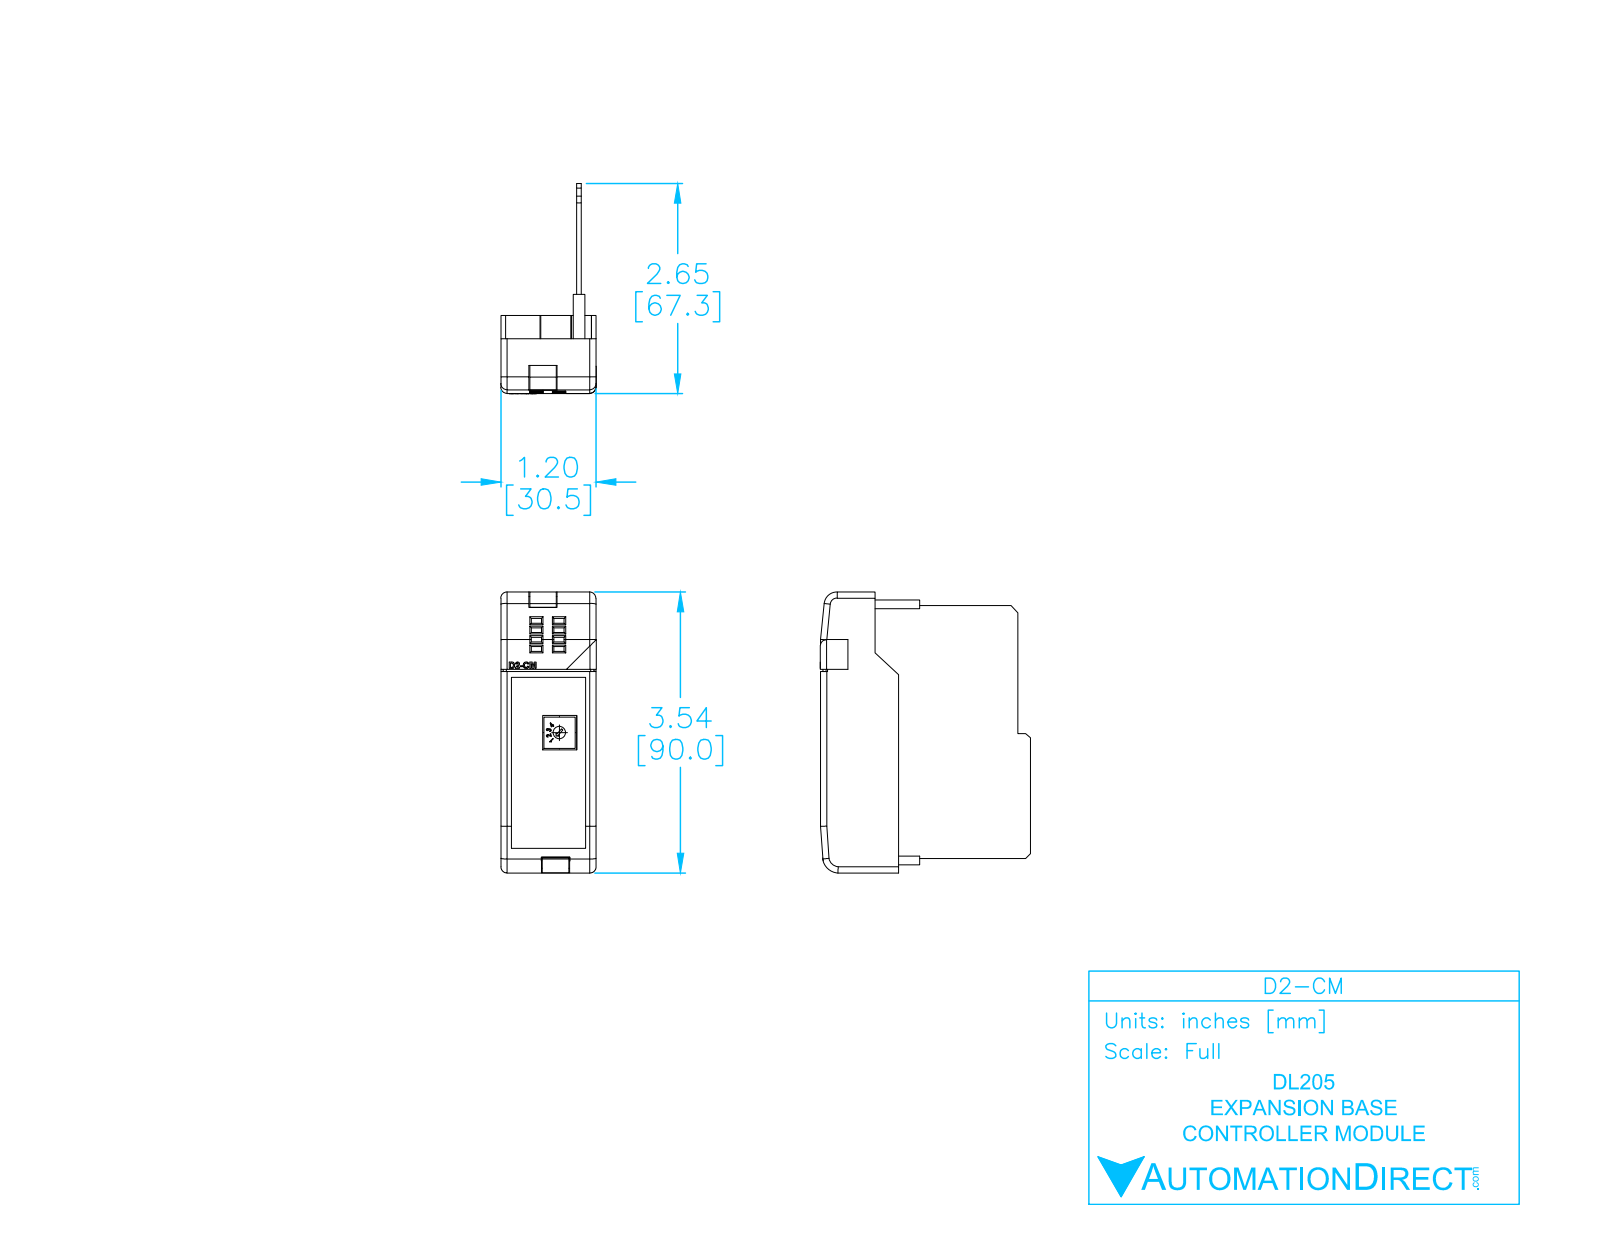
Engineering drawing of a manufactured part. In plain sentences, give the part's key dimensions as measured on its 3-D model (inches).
The part is named "D2-CM_Light_NEW". Its 3-D file was written by "SolidWorks 2009 (AUTOMOTIVE_DESIGN)". It is 3 solids with 402 faces: 256 planar, 86 cylindrical and 60 other. Overall it measures 3.543 by 2.653 by 1.203 inches. Its volume is 1.069 cubic inches and its surface area 42.13 square inches. Round bosses or shafts: 1 of diameter 0.157. Partial cylindrical surfaces (rounded edges, fillets, slot ends): 28 of radius 0.02, 11 of radius 0.079, 4 of radius 0.01, 2 of radius 0.039, 1 of radius 0.103, 1 of radius 0.149, 1 of radius 0.162, 1 of radius 0.208. The main face-to-face distances are 0.059, 0.186, 0.127, 0.245, 0.02, 0.956, 1.142, 1.015, 1.201, 0.897.
